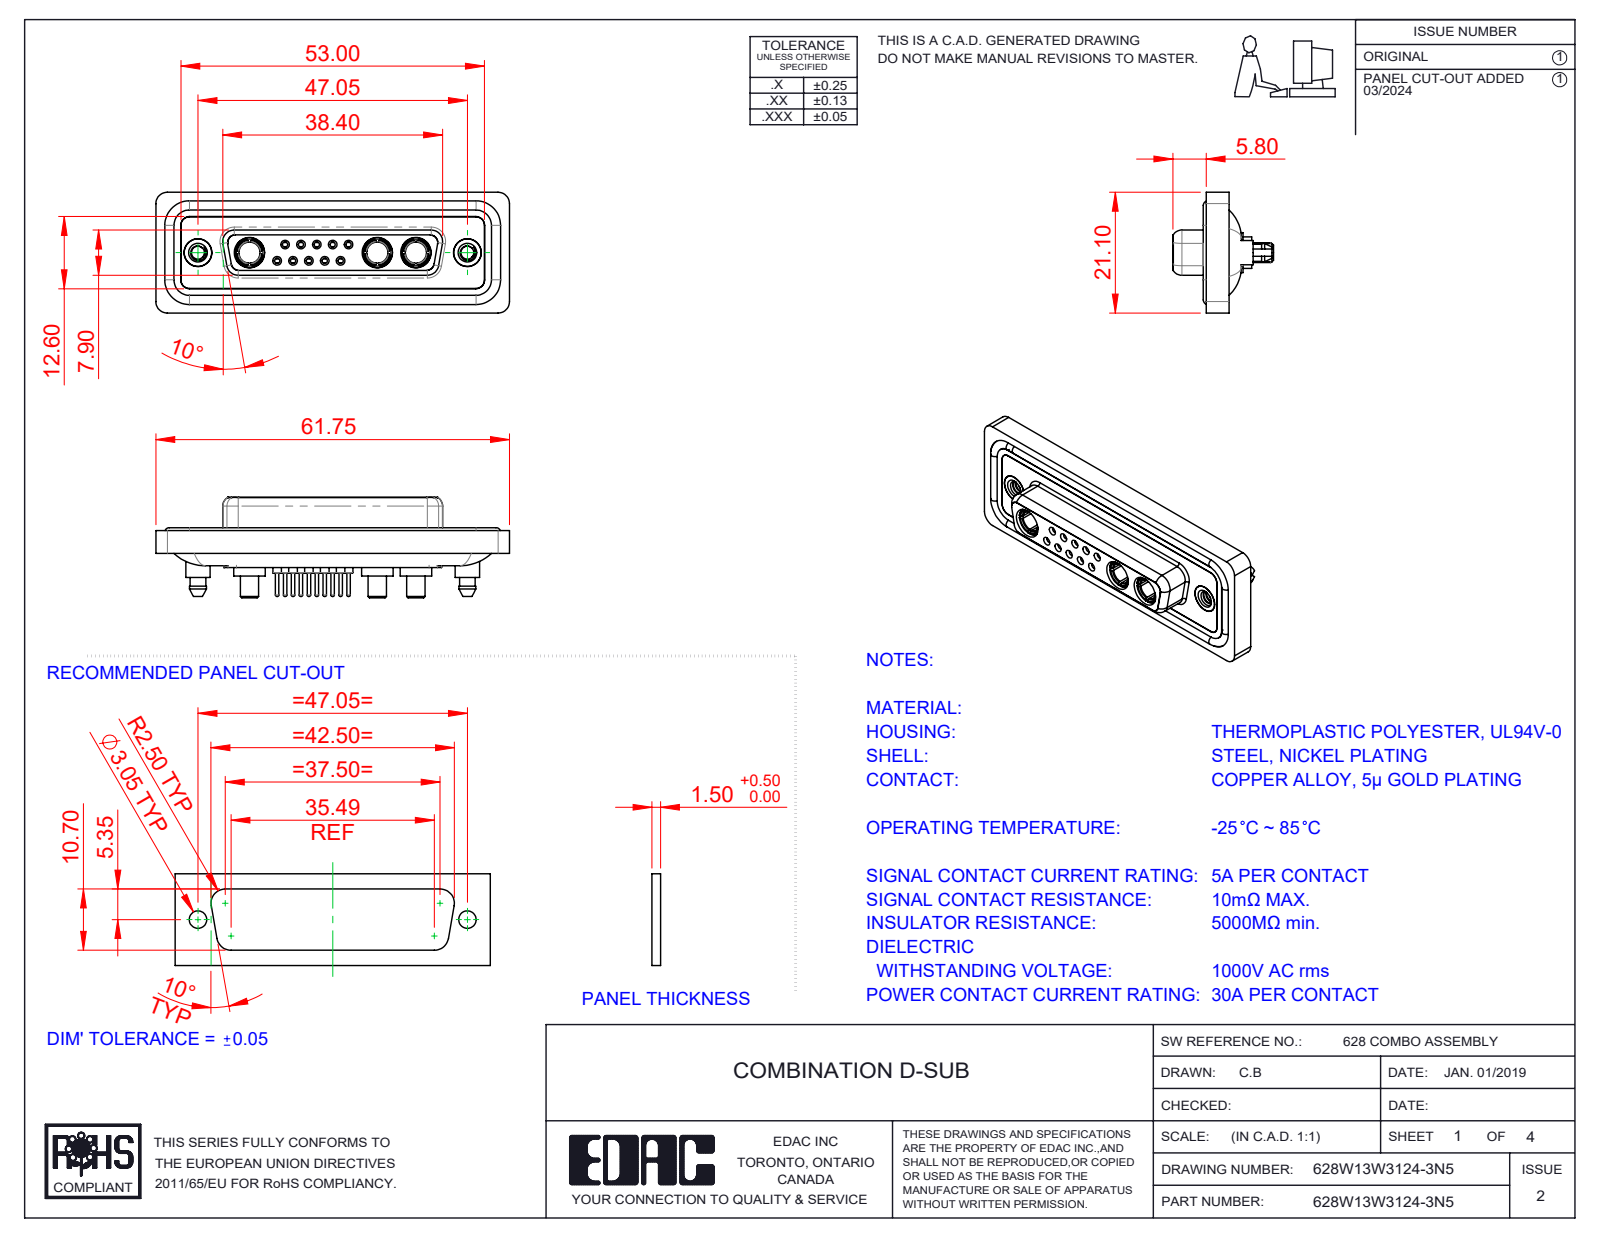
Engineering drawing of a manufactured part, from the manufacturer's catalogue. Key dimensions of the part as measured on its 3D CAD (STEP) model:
Part name (STEP PRODUCT): 628Combo Contact Row 1_24; 628Combo Waterproof Housing_25 Contacts; 628Combo Housing_13W3; 628Combo Shell Rear_25 Contacts (+5 more)
STEP written by: SolidWorks 2023 (CONFIG_CONTROL_DESIGN)
Units: millimetres
Bodies: 23 solids, 1208 faces (358 planar, 479 cylindrical, 371 other)
Overall size (bounding box): 61.75 × 21.1 × 17.55
Volume: 8 428 mm³ · Surface area: 14 055 mm²
Round holes (diameter × count): ⌀0.9 ×10, ⌀1.1 ×10, ⌀1.5 ×10, ⌀2 ×10, ⌀1.6 ×5, ⌀1.7 ×5, ⌀4.85 ×5, ⌀3.7 ×3, ⌀5.3 ×3, ⌀2.26 ×2, ⌀4 ×2, ⌀4.05 ×2
Round bosses / shafts (diameter × count): ⌀2.2 ×10, ⌀0.6 ×10, ⌀1.6 ×9, ⌀5.5 ×3, ⌀5.2 ×3, ⌀4.96 ×3, ⌀4.75 ×3, ⌀3.75 ×3
Partial cylindrical surfaces — rounded edges, fillets, slot ends (radius × count): R1.5 ×24, R2 ×18, R1.6 ×10, R1.35 ×8, R0.25 ×4, R0.5 ×4, R0.6 ×4, R0.65 ×4
Main face-to-face distances: 0.4, 1.8, 7.45, 5.65, 0.5, 6.6, 7.05, 1.6, 2.9, 1.1
Hole centre spacings: 3.16, 2.77, 5.03, 5.04, 5.54, 8.31, 7.49, 2.76
